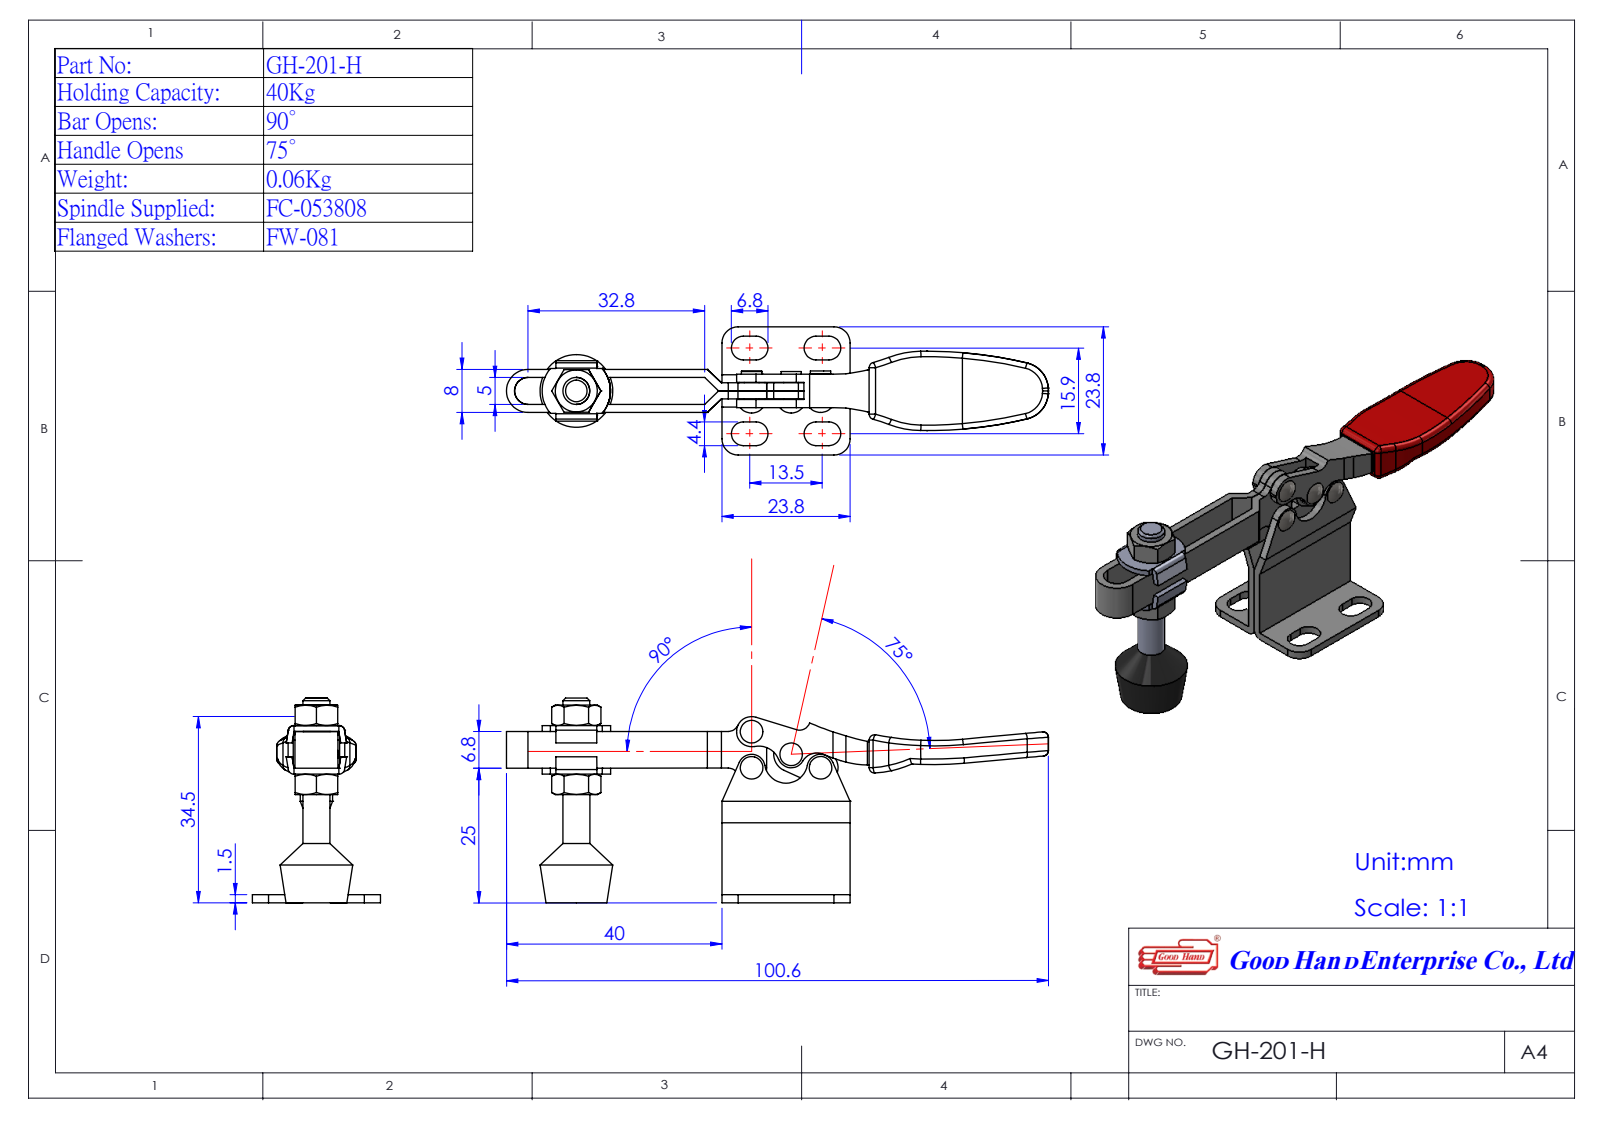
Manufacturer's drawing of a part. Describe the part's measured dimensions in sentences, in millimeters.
The part is named "101-2.508-1^GH-201-H(簡化); 120105-1^GH-201-H(簡化); Group5^GH-201-H(簡化); Group3^GH-201-H(簡化) (+2 more)". Its 3-D file was written by "SolidWorks 2016 (AUTOMOTIVE_DESIGN)". It is 6 solids with 272 faces: 121 planar, 126 cylindrical and 25 other. Overall it measures 100.6 by 38.01 by 23.8 millimeters. Its volume is 8 296 cubic millimeters and its surface area 8 869 square millimeters. Round holes: 4 of diameter 2.5. Round bosses or shafts: 4 of diameter 3.75, 4 of diameter 2.75, 1 of diameter 5. Partial cylindrical surfaces (rounded edges, fillets, slot ends): 8 of radius 2.2, 5 of radius 3, 4 of radius 1, 3 of radius 2, 3 of radius 4, 2 of radius 1.5, 2 of radius 2.5, 2 of radius 2.8. The main face-to-face distances are 1.5, 2.5, 4, 3, 1, 5.5, 6.5, 8, 0.5, 7. The hole center spacings are 6, 6.7, 7.76, 8.47, 12.8, 14.46.
